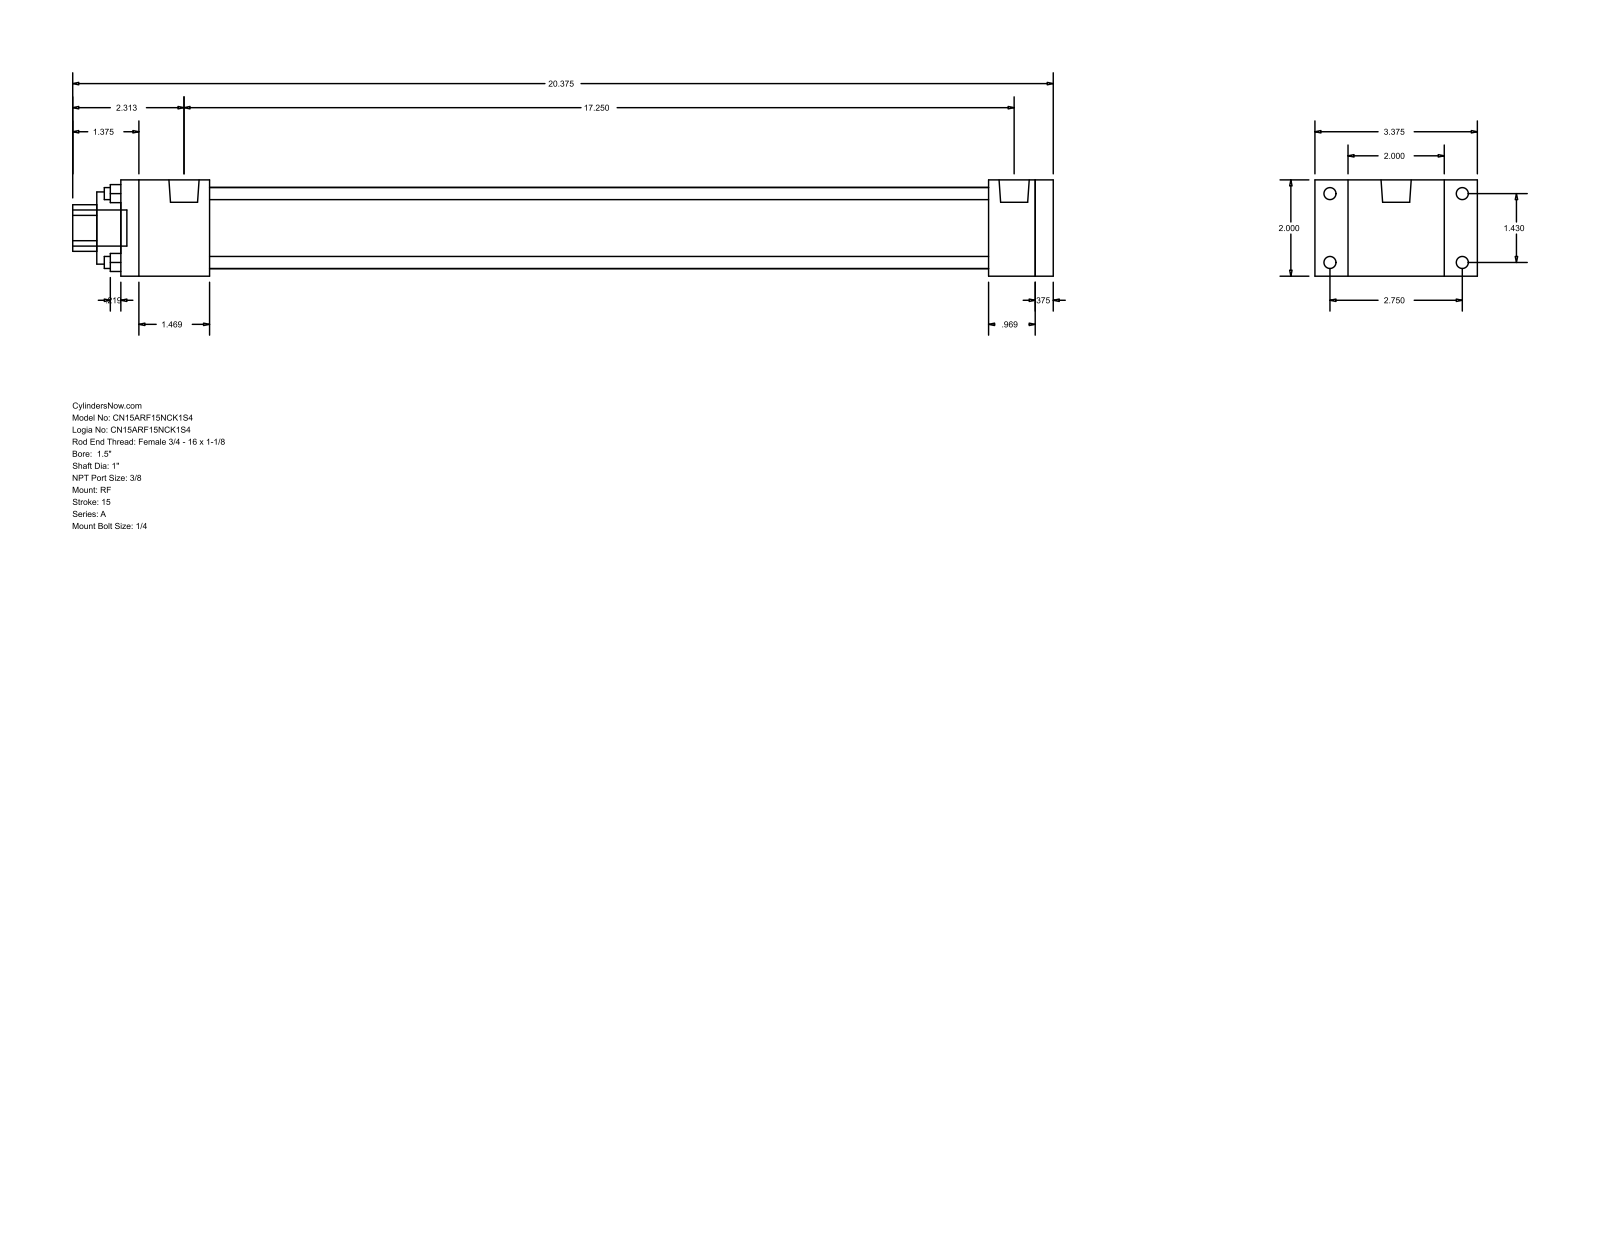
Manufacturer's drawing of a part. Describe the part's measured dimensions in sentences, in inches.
The part is named "A_RF__0150_1". Its 3-D file was written by "GSSL Pune (CONFIG_CONTROL_DESIGN)". It is 0 solids with 92 faces: 64 planar, 28 cylindrical and 0 other. Overall it measures 20.375 by 3.375 by 2 inches. Round holes: 4 of diameter 0.25, 1 of diameter 1, 1 of diameter 1.5, 1 of diameter 1.69. Round bosses or shafts: 4 of diameter 0.25, 4 of diameter 0.219, 2 of diameter 0.627, 1 of diameter 0.75. Partial cylindrical surfaces (rounded edges, fillets, slot ends): 1 of radius 0.484. The main face-to-face distances are 2, 0.375, 19, 19.375, 18.031, 0.969, 1.344, 1.844, 16.187, 17.156. The hole center spacings are 1.011, 1.43, 2.022.
